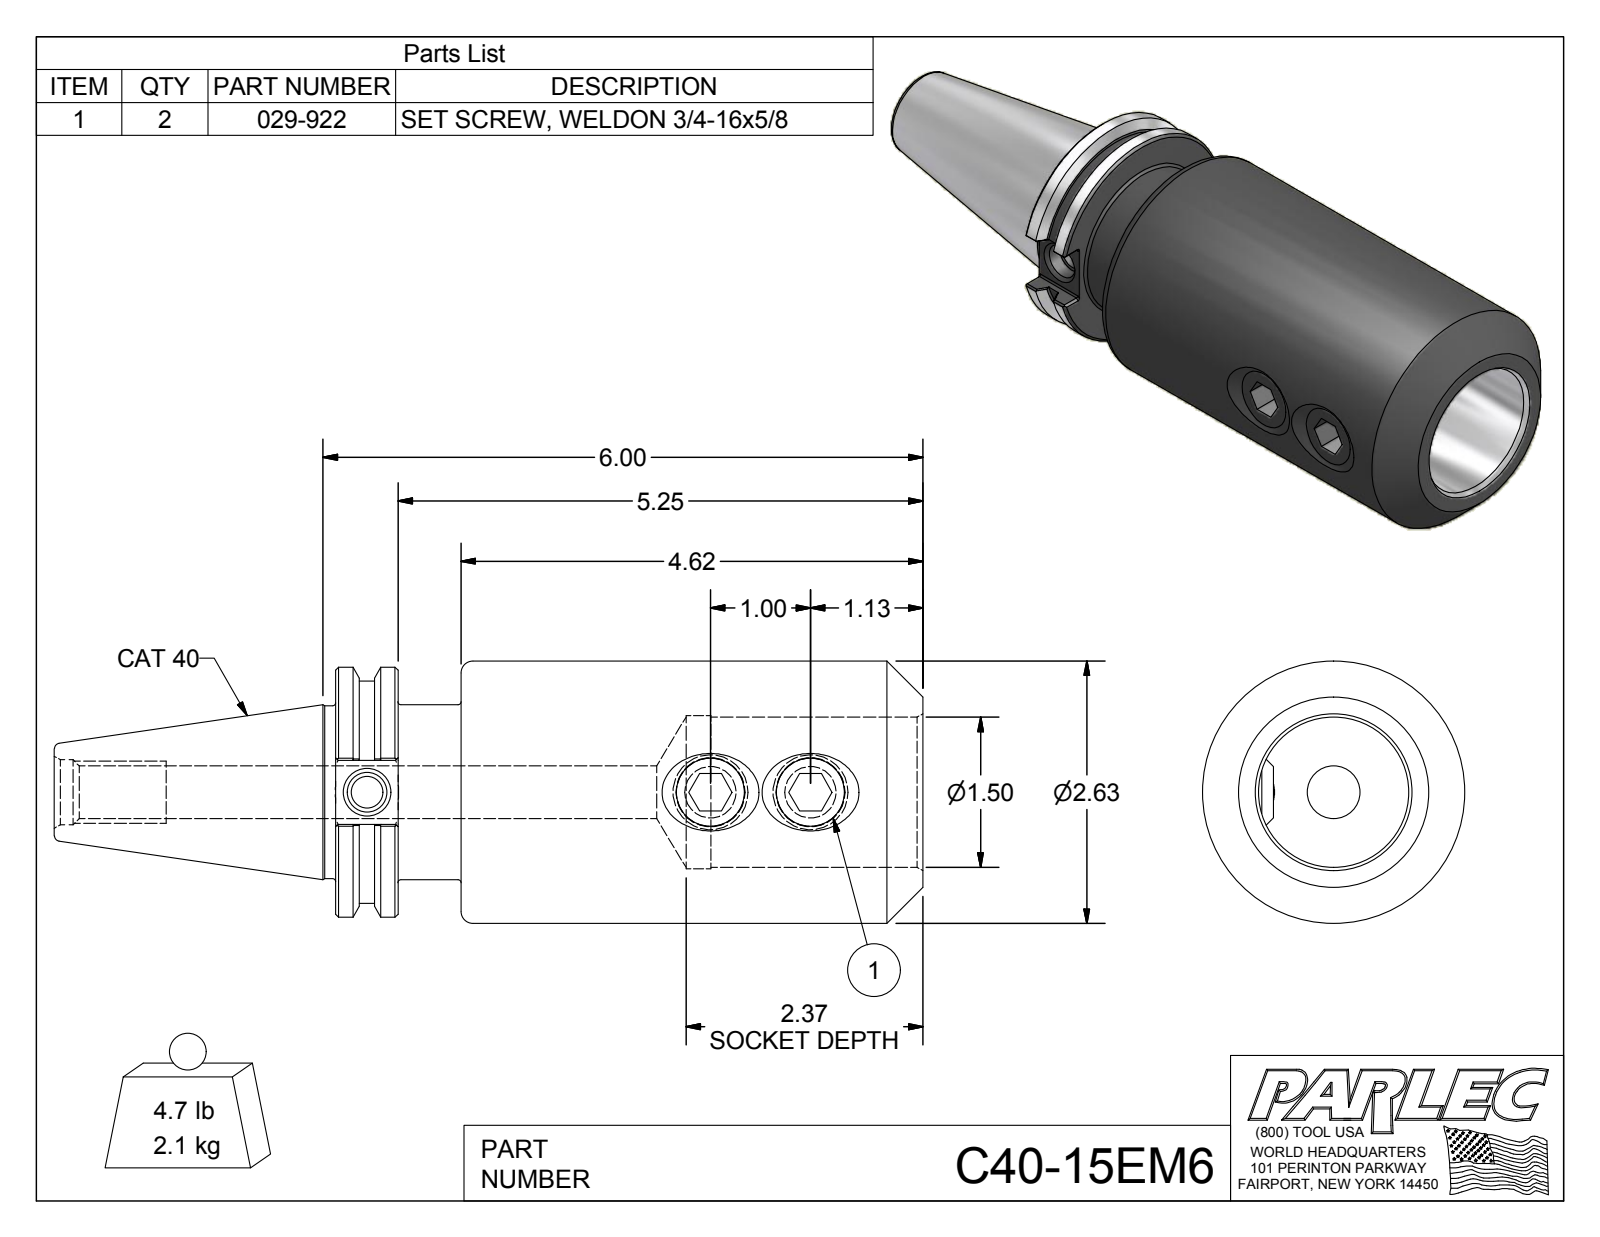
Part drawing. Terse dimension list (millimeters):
name: C40-15EM6; C40-15EM6-1; 029-922
written by: Autodesk Inventor 2012 (AUTOMOTIVE_DESIGN)
unit: mm
bodies: 3 solids, 119 faces (52 planar, 31 cylindrical, 36 other)
size: 220.6 × 66.7 × 66.7
volume: 444 100 mm³; area: 63 340 mm²
holes: 2× ⌀17.3, 1× ⌀8, 1× ⌀10.1, 1× ⌀13.4, 1× ⌀16.5, 1× ⌀38.1, 1× ⌀38.9
bosses: 2× ⌀19.1, 1× ⌀66.7, 1× ⌀63.5, 1× ⌀56.4, 1× ⌀44.5, 1× ⌀43.9
rounds: 12× R0.5
face distances: 31.9, 15.9, 16, 149.2, 133.4, 117.3, 15.9, 9.5, 37.8, 53.7
hole spacings: 25.4, 87.2, 112.6
